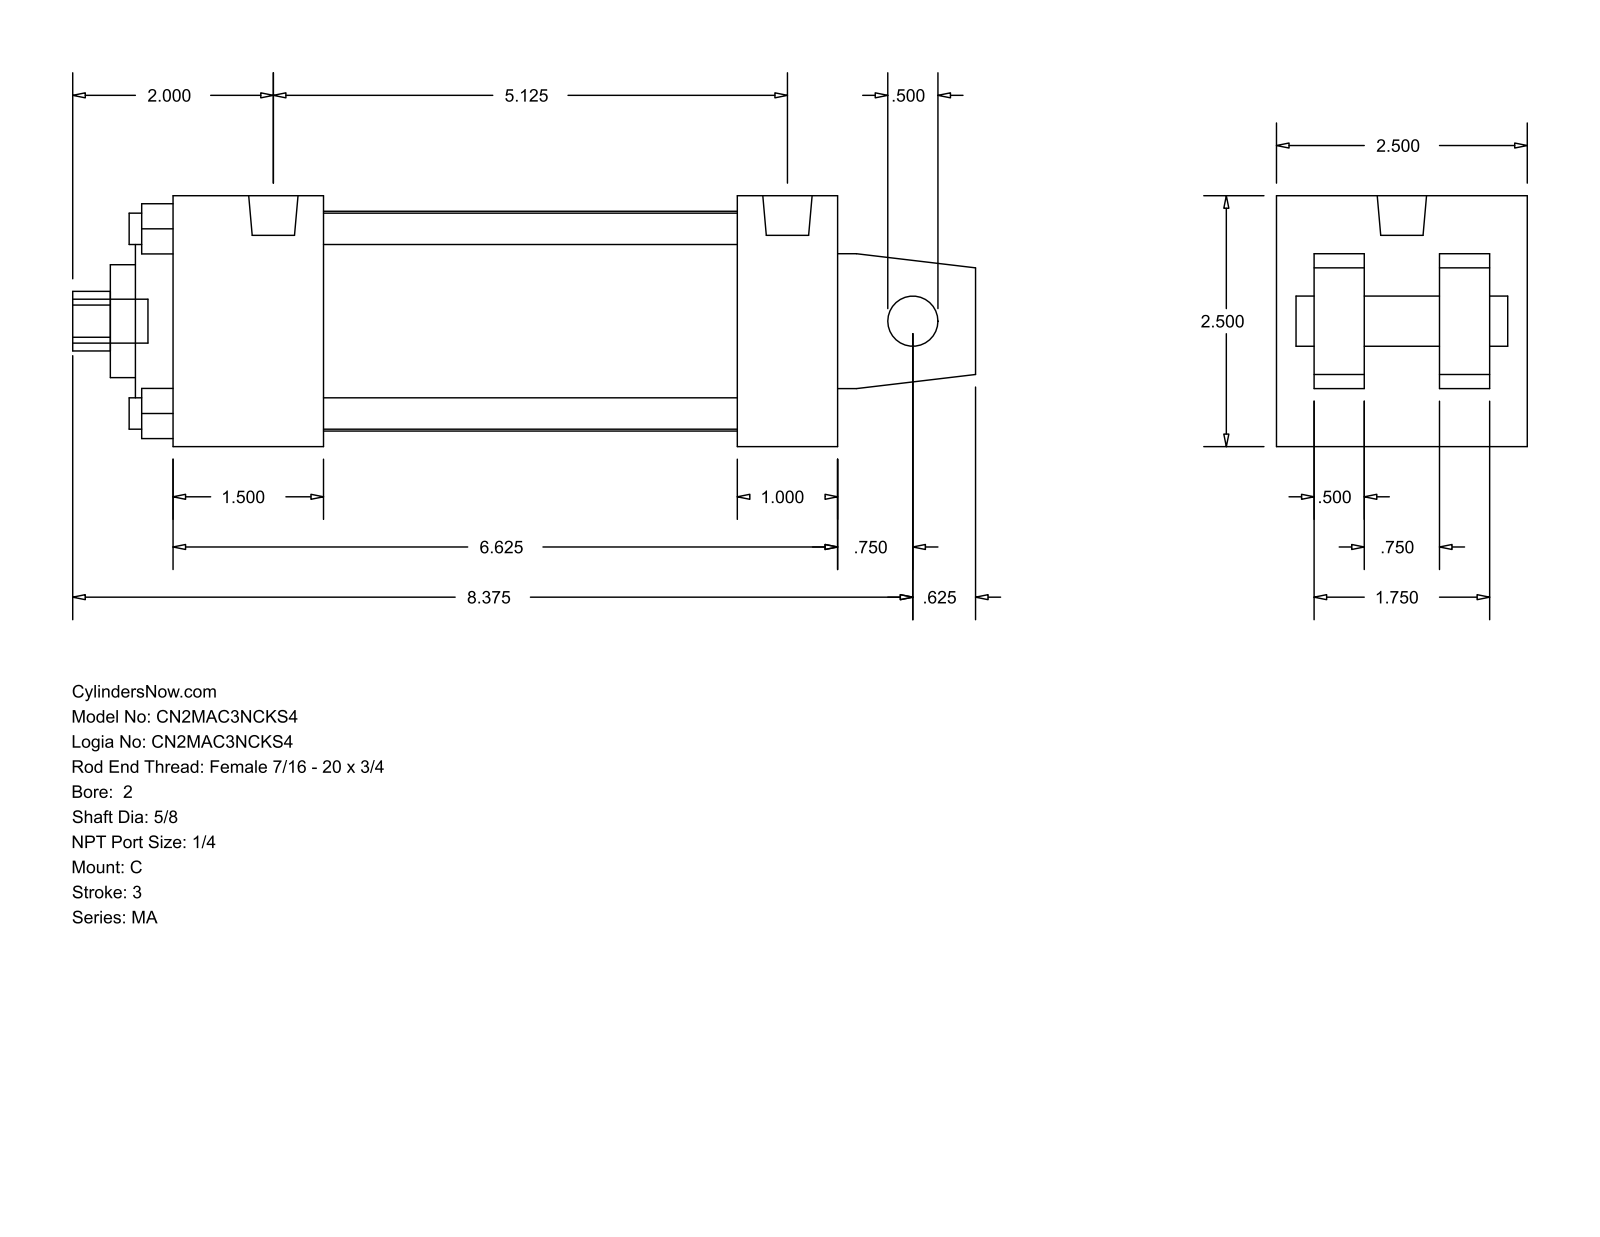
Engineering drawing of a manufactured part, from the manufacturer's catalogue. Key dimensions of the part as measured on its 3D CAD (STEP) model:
Part name (STEP PRODUCT): MA_C__0200_0.625
STEP written by: GSSL Pune (CONFIG_CONTROL_DESIGN)
Units: millimetres
Bodies: 0 solids, 105 faces (77 planar, 28 cylindrical, 0 other)
Overall size (bounding box): 228.6 × 63.5 × 63.5
Round holes (diameter × count): ⌀7.94 ×4, ⌀12.7 ×1, ⌀15.88 ×1, ⌀28.57 ×1, ⌀50.8 ×1, ⌀55.63 ×1
Round bosses / shafts (diameter × count): ⌀7.94 ×4, ⌀12.49 ×2, ⌀11.11 ×1
Partial cylindrical surfaces — rounded edges, fillets, slot ends (radius × count): R7.54 ×1
Main face-to-face distances: 63.5, 9.52, 12.7, 22.22, 41.28, 53.98, 31.76, 25.4, 38.1, 168.28
Hole centre spacings: 33.05, 46.74, 66.1
